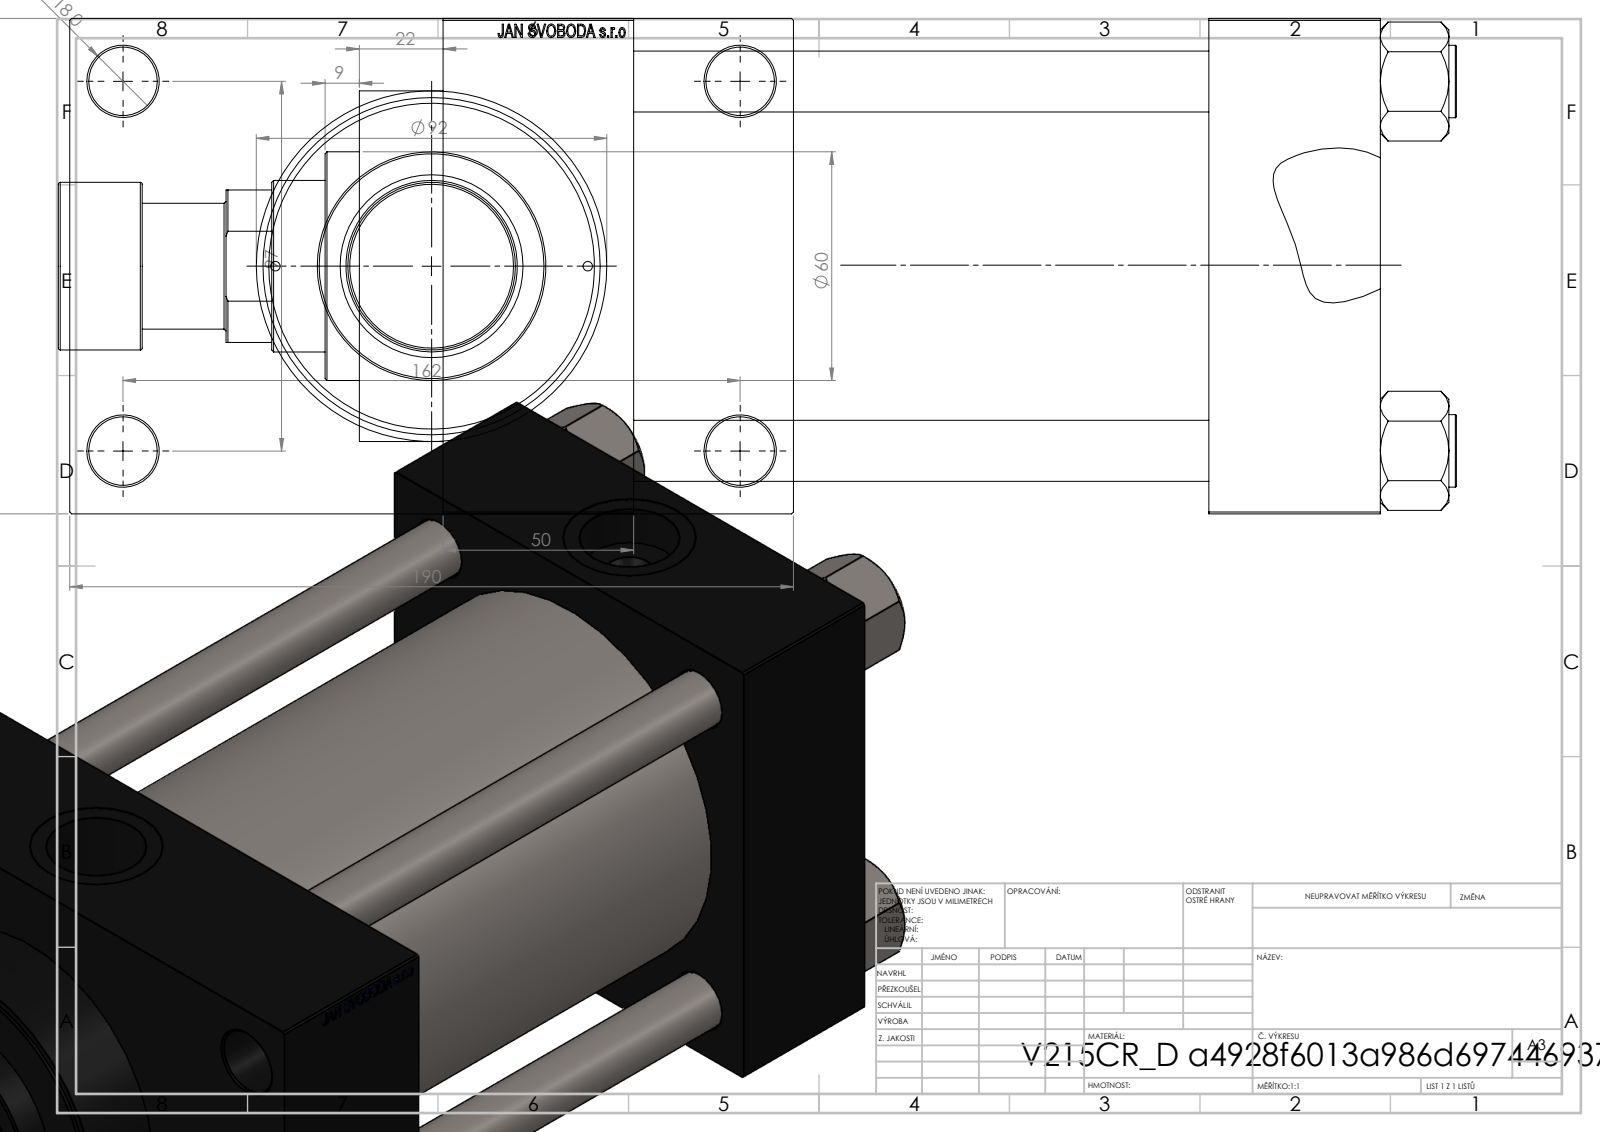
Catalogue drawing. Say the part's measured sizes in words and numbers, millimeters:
The part is named "V215_VC_A; V215CR_D_Body; V215CR_ROD_END_F; V215CR_VCP_D (+2 more)". Its 3-D file was written by "SolidWorks 2019 (CONFIG_CONTROL_DESIGN)". It is 12 solids with 1173 faces: 550 planar, 97 cylindrical and 526 other. Overall it measures 367 by 190 by 130 millimeters. Its volume is 2 928 000 cubic millimeters and its surface area 439 786 square millimeters. Round holes: 4 of diameter 16, 4 of diameter 18, 2 of diameter 2.5, 2 of diameter 7, 2 of diameter 26.44, 2 of diameter 35, 1 of diameter 31.5, 1 of diameter 45, 1 of diameter 48, 1 of diameter 76, 1 of diameter 85.5, 1 of diameter 100. Round bosses or shafts: 4 of diameter 19, 1 of diameter 106, 1 of diameter 92, 1 of diameter 60, 1 of diameter 44, 1 of diameter 33. The main face-to-face distances are 130, 151, 45, 196, 246, 201, 50, 30, 160, 190. The hole center spacings are 32.55, 49.02, 62.87, 68.52, 94.41, 96.9, 101.73, 102.27.
